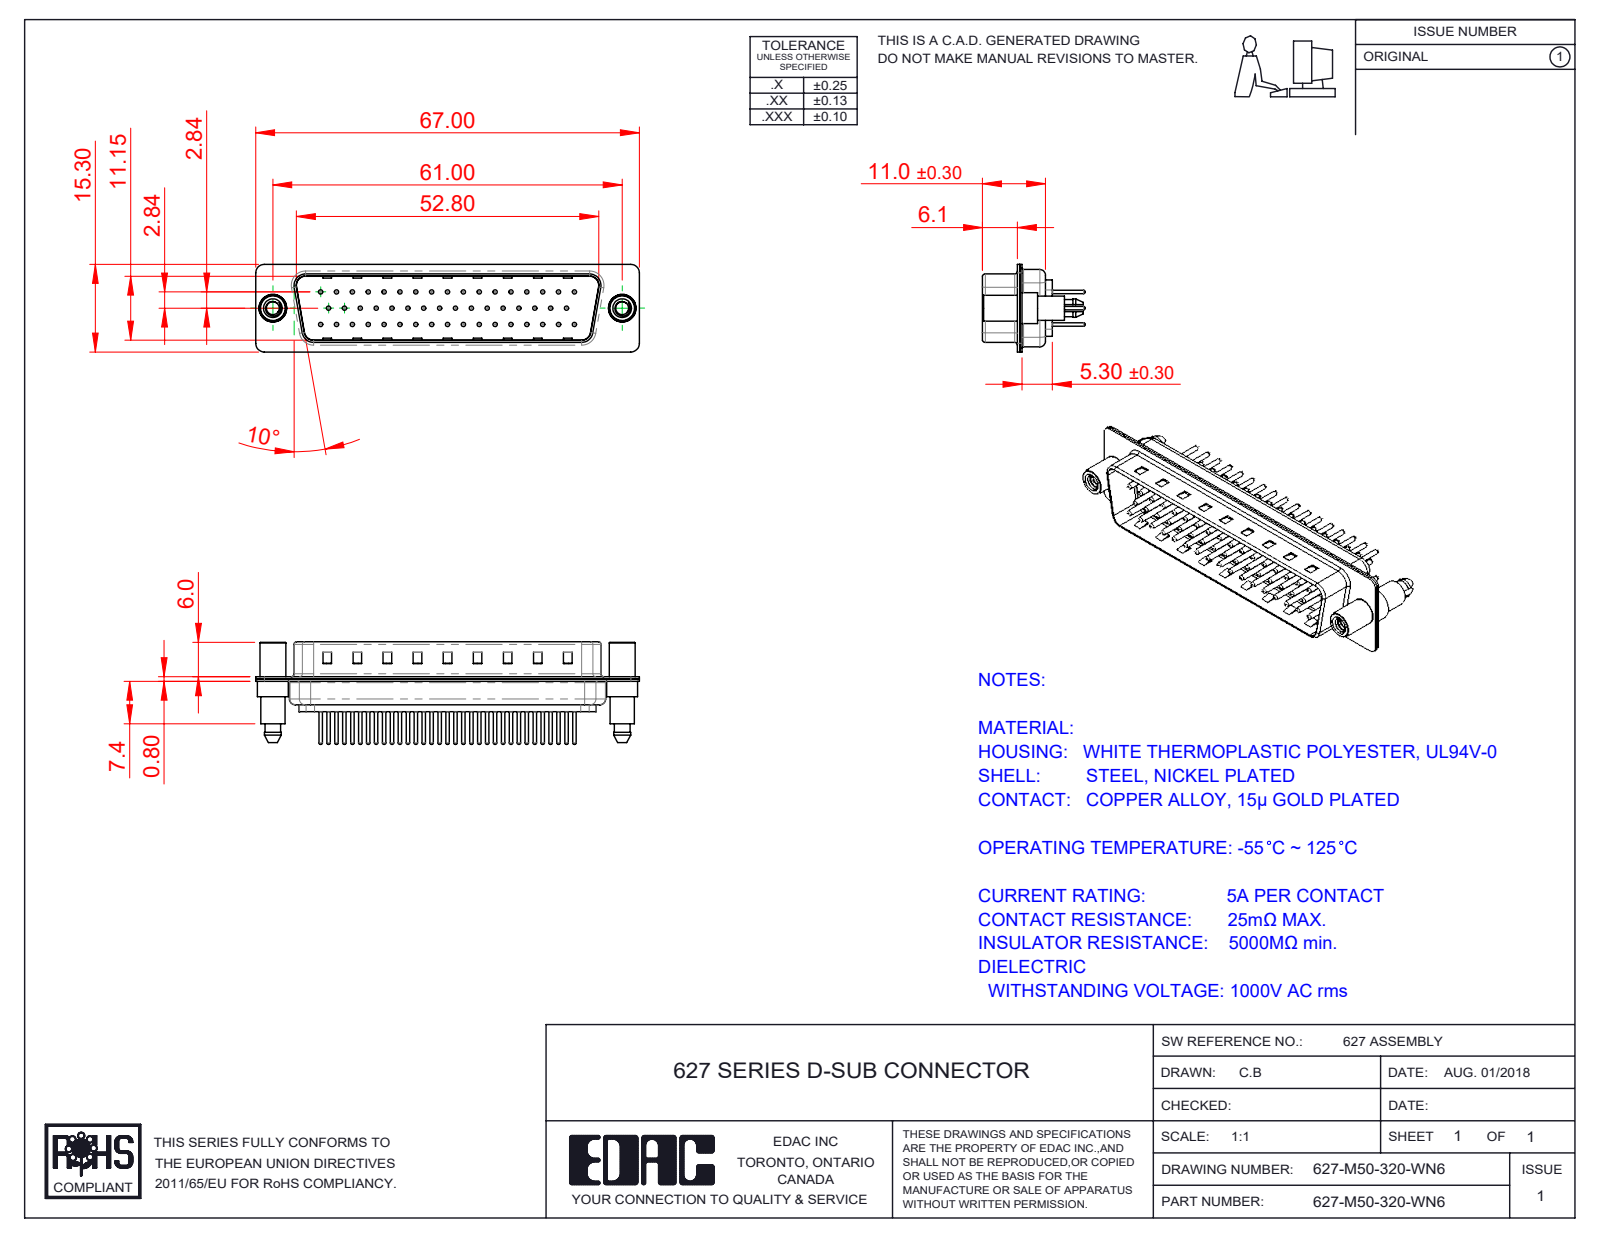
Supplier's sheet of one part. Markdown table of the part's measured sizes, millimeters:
| quantity | value |
| --- | --- |
| part name | 627M Contact Row 2_20; 627M Contact Row 3_20; 627-M50-320-WN6; 627M 4-40 Threaded Standoff and Boardlock (+4 more) |
| STEP written by | SolidWorks 2020 (CONFIG_CONTROL_DESIGN) |
| units | millimeters |
| bodies | 55 solids, 2314 faces (571 planar, 869 cylindrical, 874 other) |
| overall size | 67 × 17.9 × 15.3 |
| volume | 4 863 mm³ |
| surface area | 11 167 mm² |
| round holes (diameter × count) | 0.75 × 50, 1.6 × 50, 2 × 50, 2.26 × 2, 4 × 2, 4.8 × 2 |
| round bosses / shafts (diameter × count) | 1.5 × 50, 0.6 × 50, 5.4 × 2, 4.9 × 2, 4.5 × 2, 4.25 × 2 |
| partial cylindrical surfaces (radius × count) | 1.5 × 18, 2 × 12, 1.6 × 10, 0.5 × 8, 0.25 × 4, 0.6 × 4, 0.65 × 4, 0.9 × 4 |
| main face-to-face distances | 0.4, 11.55, 5.7, 6.1, 0.78, 0.77, 12.33, 5.3, 12.32, 13.1 |
| hole center spacings | 3.16, 2.77, 5.54, 8.31, 11.08, 13.85, 16.62, 5.03 |
